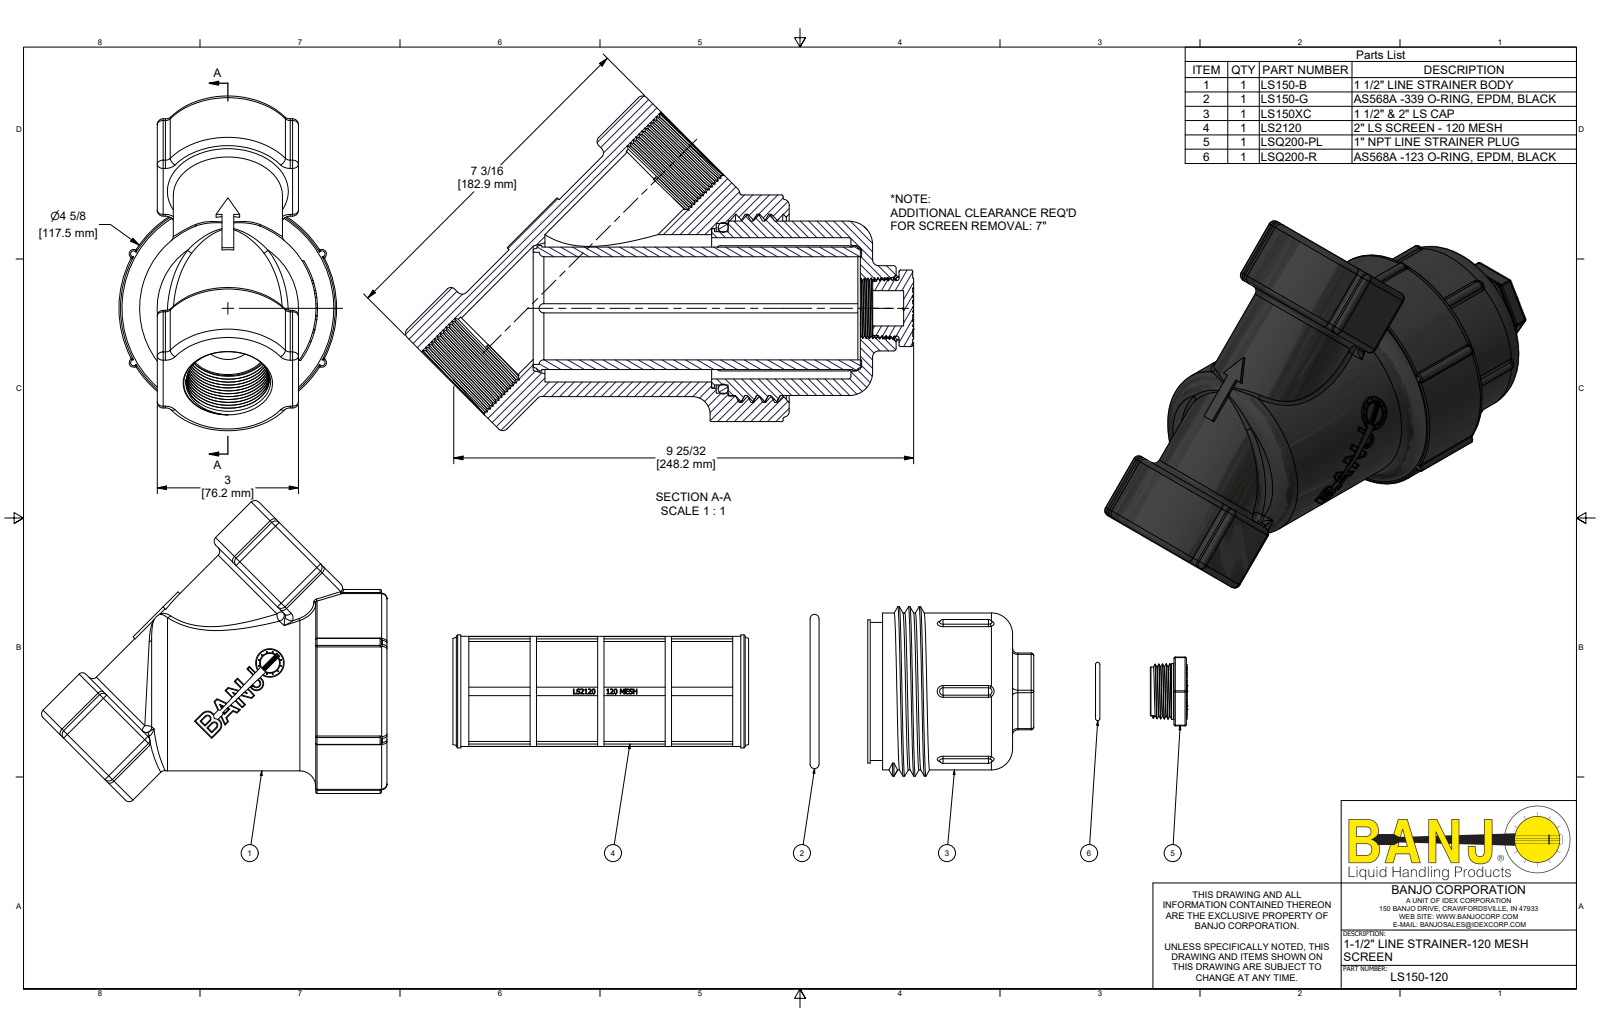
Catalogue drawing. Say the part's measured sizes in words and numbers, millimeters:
The part is named "LS150-120; LS150-B; LS150-C; LS150XC (+4 more)". Its 3-D file was written by "Autodesk Inventor 2022 (AUTOMOTIVE_DESIGN)". It is 6 solids with 1758 faces: 875 planar, 302 cylindrical and 581 other. Overall it measures 274.3 by 180.6 by 117.5 millimeters. Its volume is 958 000 cubic millimeters and its surface area 309 500 square millimeters. Round holes: 2 of diameter 43.2, 2 of diameter 44.7, 1 of diameter 11.5, 1 of diameter 16.3, 1 of diameter 19.1, 1 of diameter 55.6, 1 of diameter 59.7, 1 of diameter 76.2, 1 of diameter 79.5, 1 of diameter 86.2, 1 of diameter 91.6, 1 of diameter 94.7. Round bosses or shafts: 1 of diameter 117.5, 1 of diameter 101.6, 1 of diameter 95.3, 1 of diameter 94, 1 of diameter 85.9, 1 of diameter 82.7, 1 of diameter 67.7, 1 of diameter 66. Partial cylindrical surfaces (rounded edges, fillets, slot ends): 46 of radius 1.5, 35 of radius 3.2, 30 of radius 0.8, 12 of radius 2.4, 4 of radius 2.5, 4 of radius 2.8, 2 of radius 1.7, 2 of radius 2.1. The main face-to-face distances are 40.5, 36.7, 76.2, 182.9, 80.3, 176.6, 96.3, 34, 5.1, 38.4.
